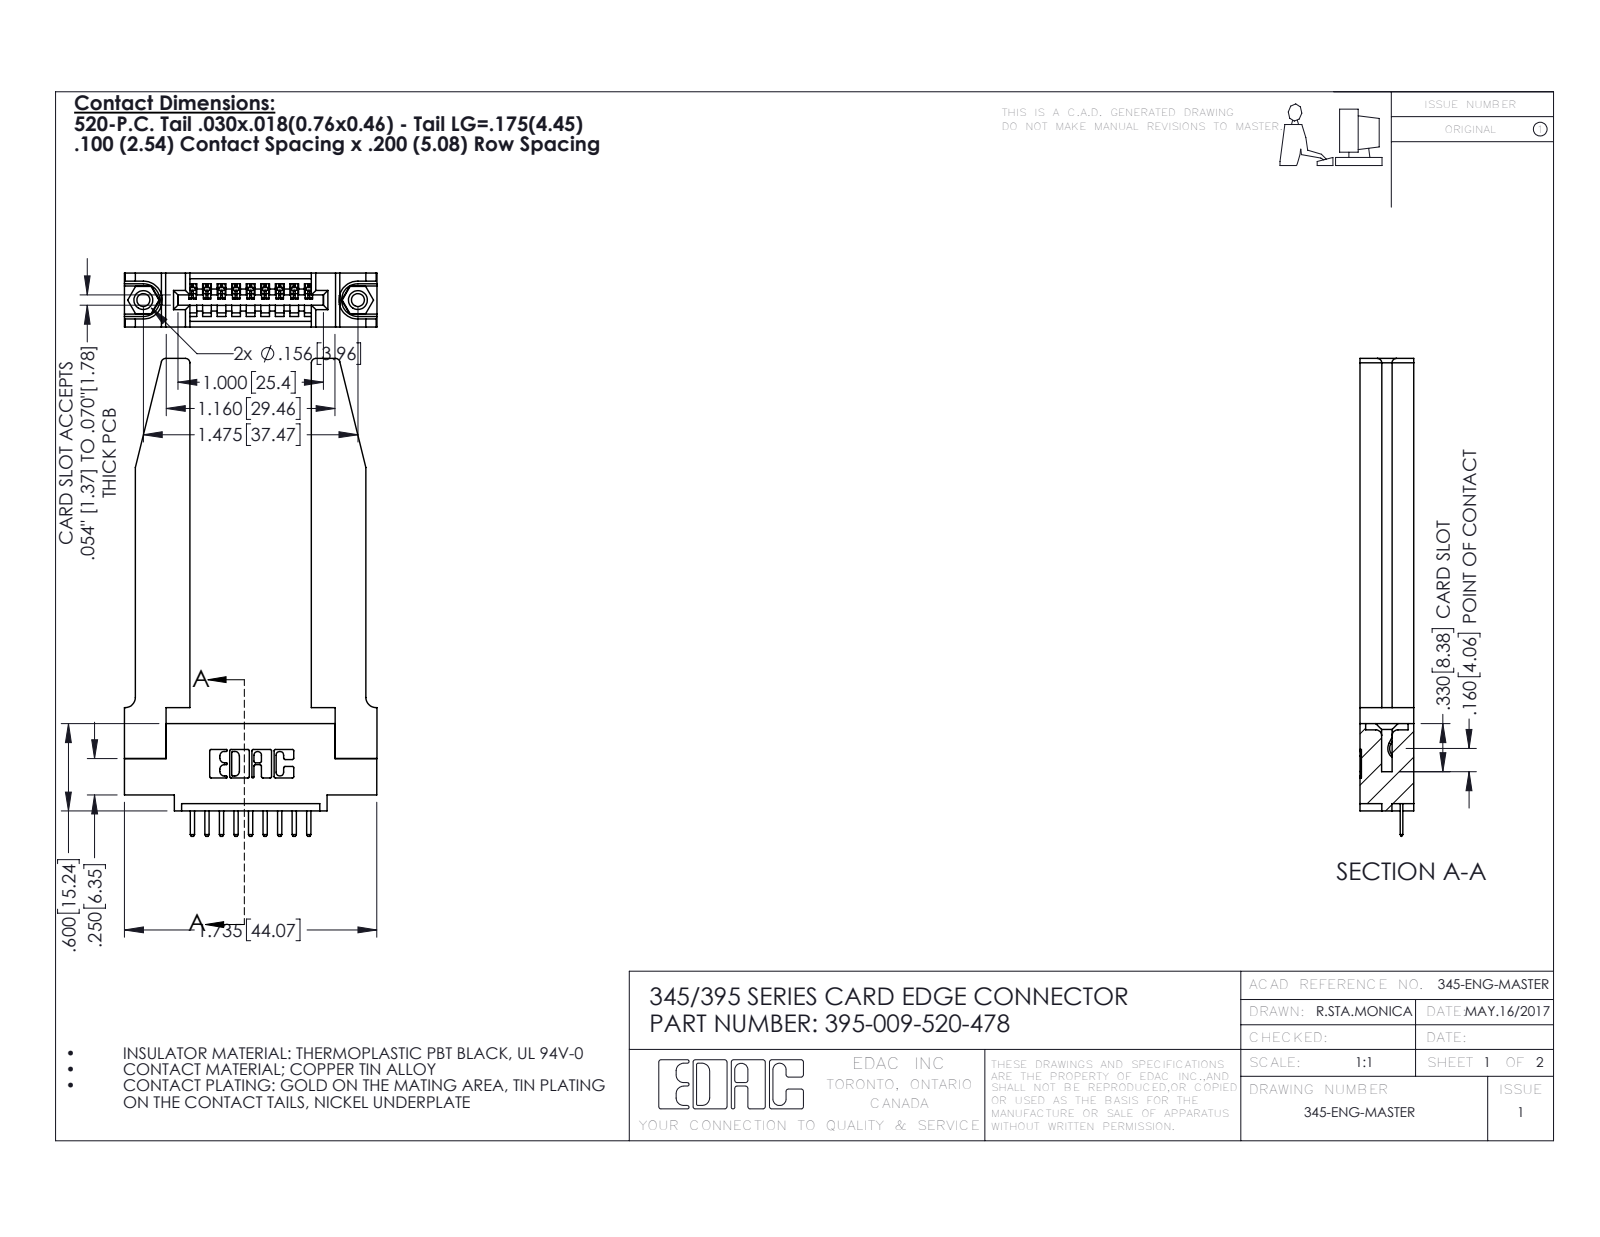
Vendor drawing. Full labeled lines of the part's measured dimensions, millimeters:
Part name (STEP PRODUCT): 345-250-001_345-250-001-102; 395-009-520-478; 345 Part_0.110 Offset - 0.156 Dia-TH; 345-292-001_345-293-120 (+1 more)
STEP written by: SolidWorks 2016 (CONFIG_CONTROL_DESIGN)
Units: millimetres
Bodies: 14 solids, 922 faces (604 planar, 266 cylindrical, 52 other)
Overall size (bounding box): 83.4 × 44.1 × 9.4
Volume: 11 600 mm³ · Surface area: 11 470 mm²
Round holes (diameter × count): ⌀2.3 ×2, ⌀3.2 ×2, ⌀4 ×2, ⌀1.6 ×1
Round bosses / shafts (diameter × count): ⌀3.9 ×2
Partial cylindrical surfaces — rounded edges, fillets, slot ends (radius × count): R0.3 ×22, R0.3 ×20, R0.2 ×18, R0.8 ×8, R0.2 ×6, R0.8 ×6, R0.7 ×3, R0.8 ×2
Main face-to-face distances: 9.4, 3.8, 1.8, 3.8, 5.6, 7.6, 2, 21.2, 1.8, 1.4
Hole centre spacings: 6.9, 31.6, 37.5
